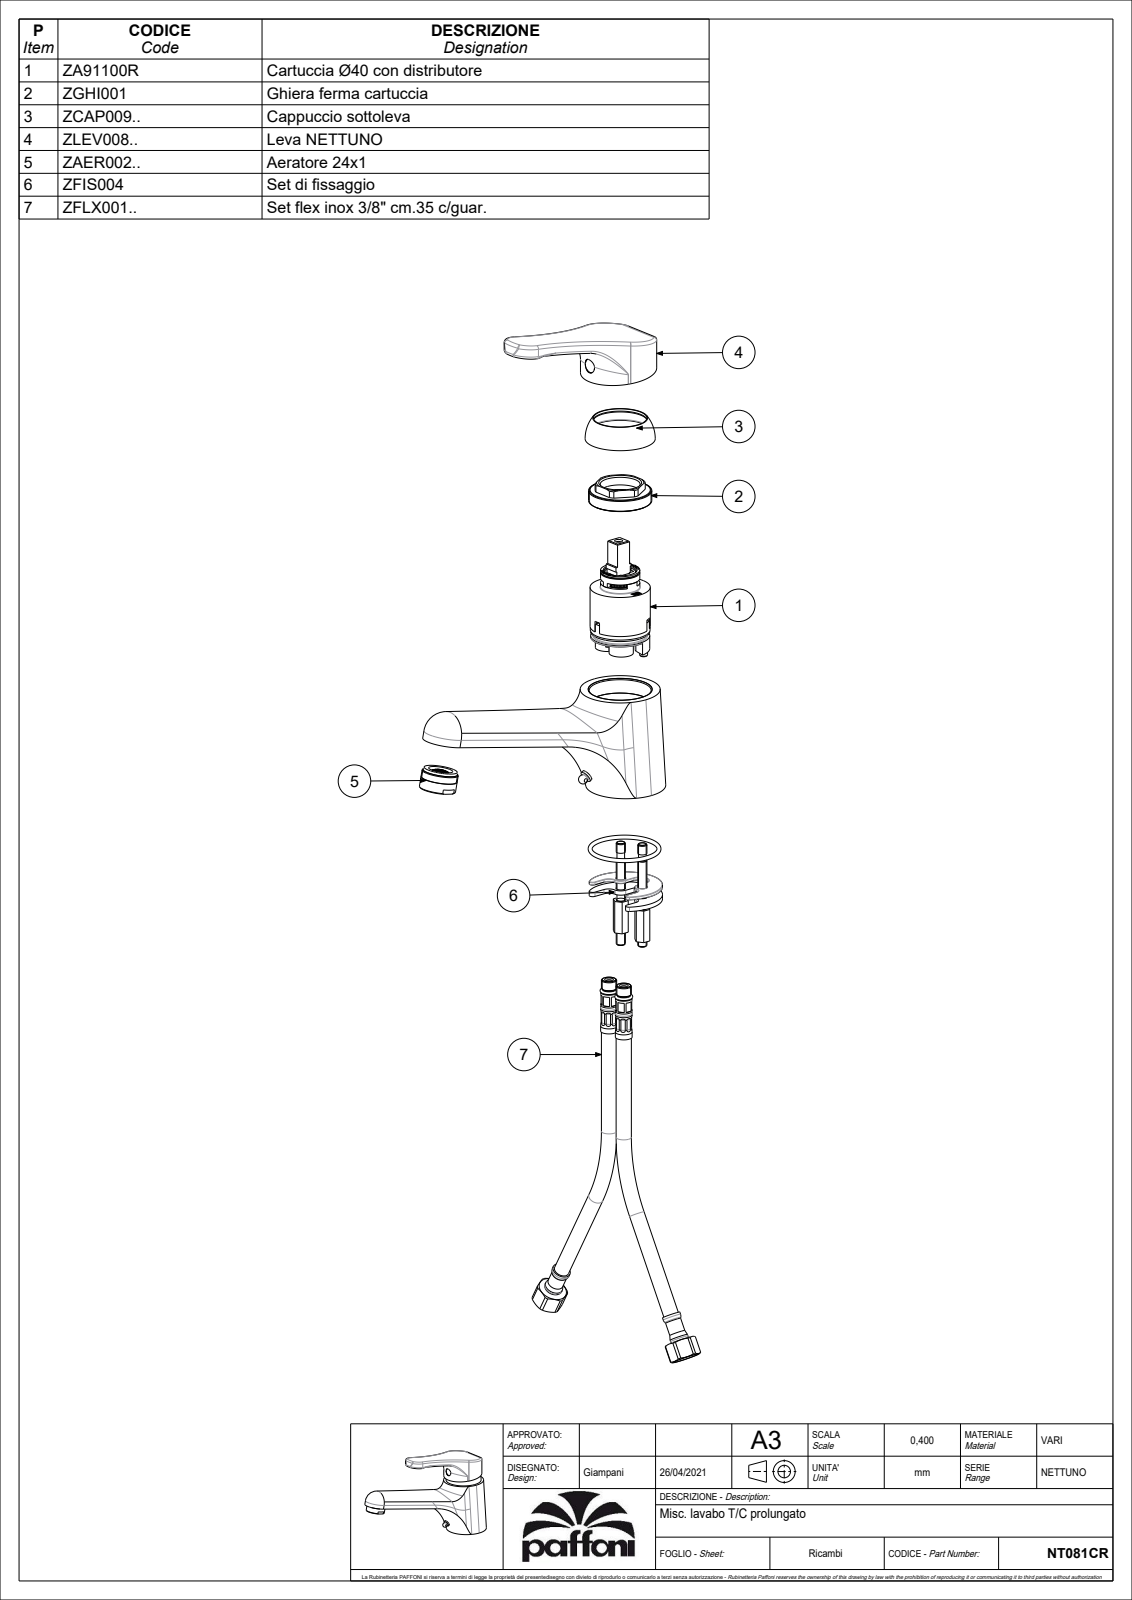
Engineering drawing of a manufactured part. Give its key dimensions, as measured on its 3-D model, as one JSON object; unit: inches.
{"part_name": "NT081CR", "step_written_by": "CREO PARAMETRIC BY PTC INC, 2020044 (CONFIG_CONTROL_DESIGN)", "units": "inches", "bodies": {"solids": 1, "faces": 283, "planar": 53, "cylindrical": 83, "other": 147}, "overall_size": [7.694, 4.596, 2.067], "volume_in3": 11.31, "surface_area_in2": 111.9, "round_holes": [[0.197, 2], [0.217, 2], [0.276, 2], [0.354, 2], [0.433, 2], [0.37, 1], [0.63, 1], [0.787, 1], [0.827, 1], [0.906, 1], [0.965, 1], [1.539, 1]], "round_bosses_or_shafts": [[0.394, 2], [1.969, 1], [1.654, 1], [0.945, 1], [0.315, 1], [0.177, 1]], "partial_cylinders_radius": [[0.098, 6], [0.079, 4], [0.197, 2], [0.295, 2], [5.315, 2], [0.039, 1], [0.394, 1], [0.512, 1]], "face_to_face_distances": [0.689, 0.846, 0.118, 0.157, 2.675, 1.299, 0.313, 0.256, 1.829, 1.986], "hole_center_spacings": [0.041, 0.072, 0.322, 0.339, 0.432, 0.473, 0.476, 0.515]}
